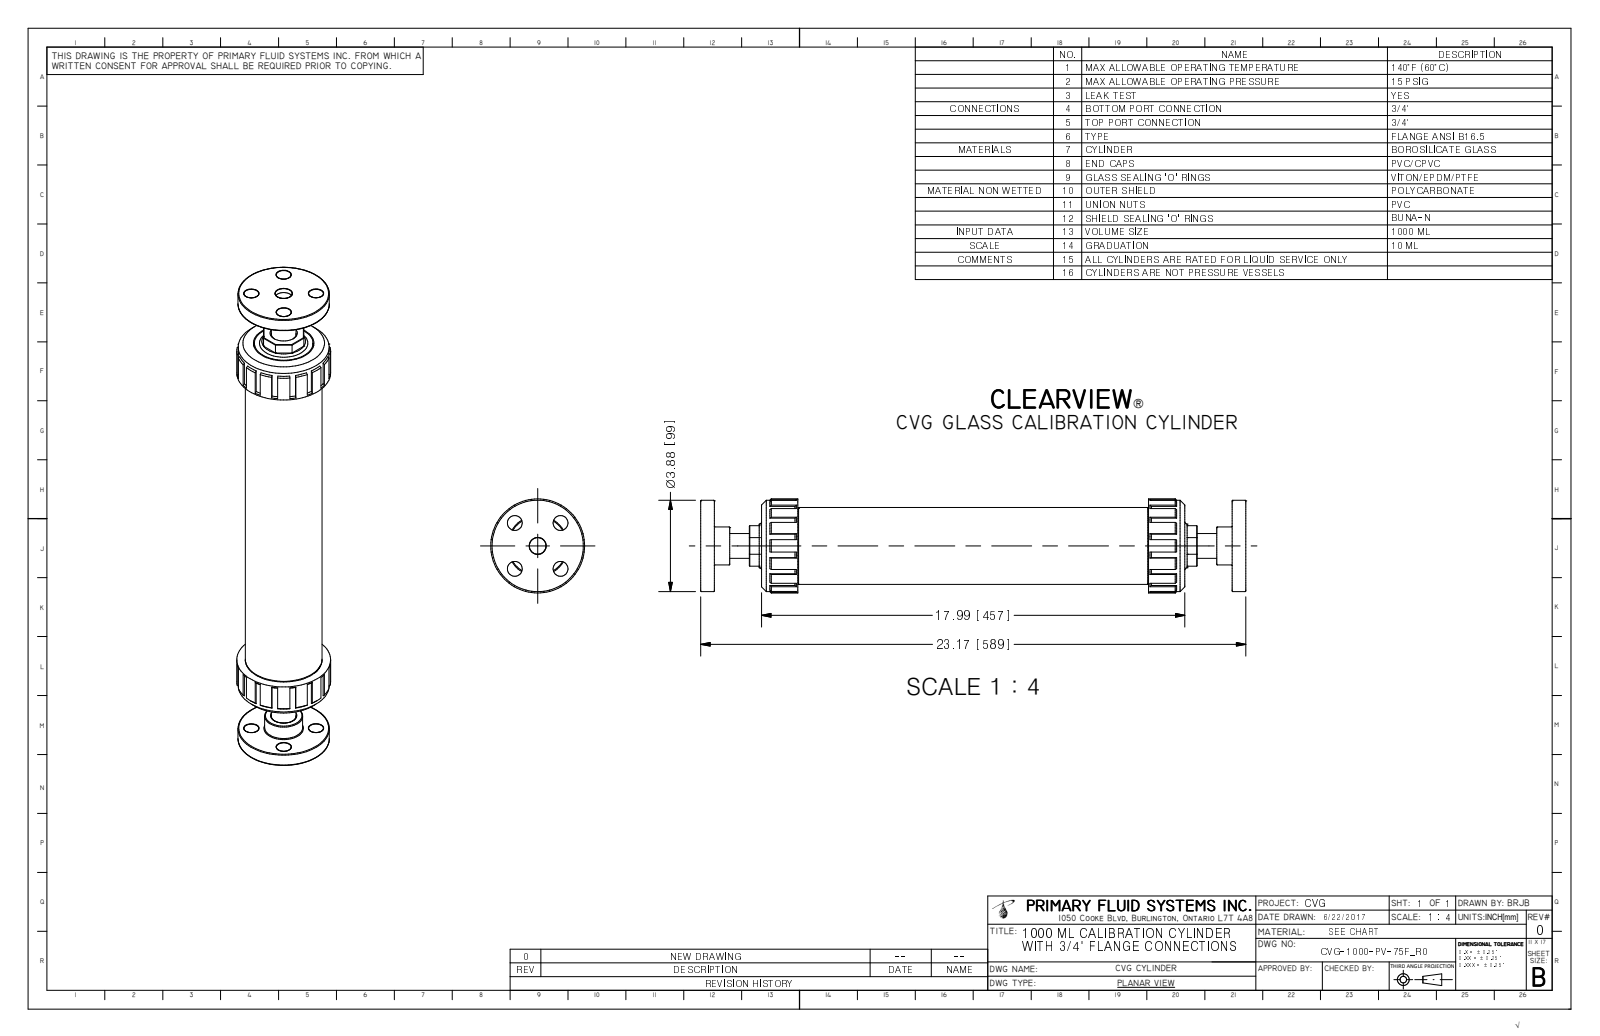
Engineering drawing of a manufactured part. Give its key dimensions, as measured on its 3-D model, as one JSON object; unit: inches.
{"part_name": "CVG-1000-PV-75F_R0", "step_written_by": "Autodesk Inventor 2009 (AUTOMOTIVE_DESIGN)", "units": "inches", "bodies": {"solids": 1, "faces": 291, "planar": 152, "cylindrical": 32, "other": 107}, "overall_size": [23.17, 3.99, 3.99], "volume_in3": 178.7, "surface_area_in2": 334.3, "round_holes": [[0.63, 4], [0.722, 1], [0.742, 1], [2.57, 1]], "round_bosses_or_shafts": [[3.99, 1], [3.88, 1], [3.87, 1], [3.265, 1], [3.225, 1], [2.495, 1], [1.616, 1], [1.05, 1]], "partial_cylinders_radius": [[1.553, 1]], "face_to_face_distances": [23.17, 1.54, 16.452, 0.575, 22.595, 22.595, 22.02, 0.575, 19.04, 2.588], "hole_center_spacings": [1.375, 1.945, 2.75]}
